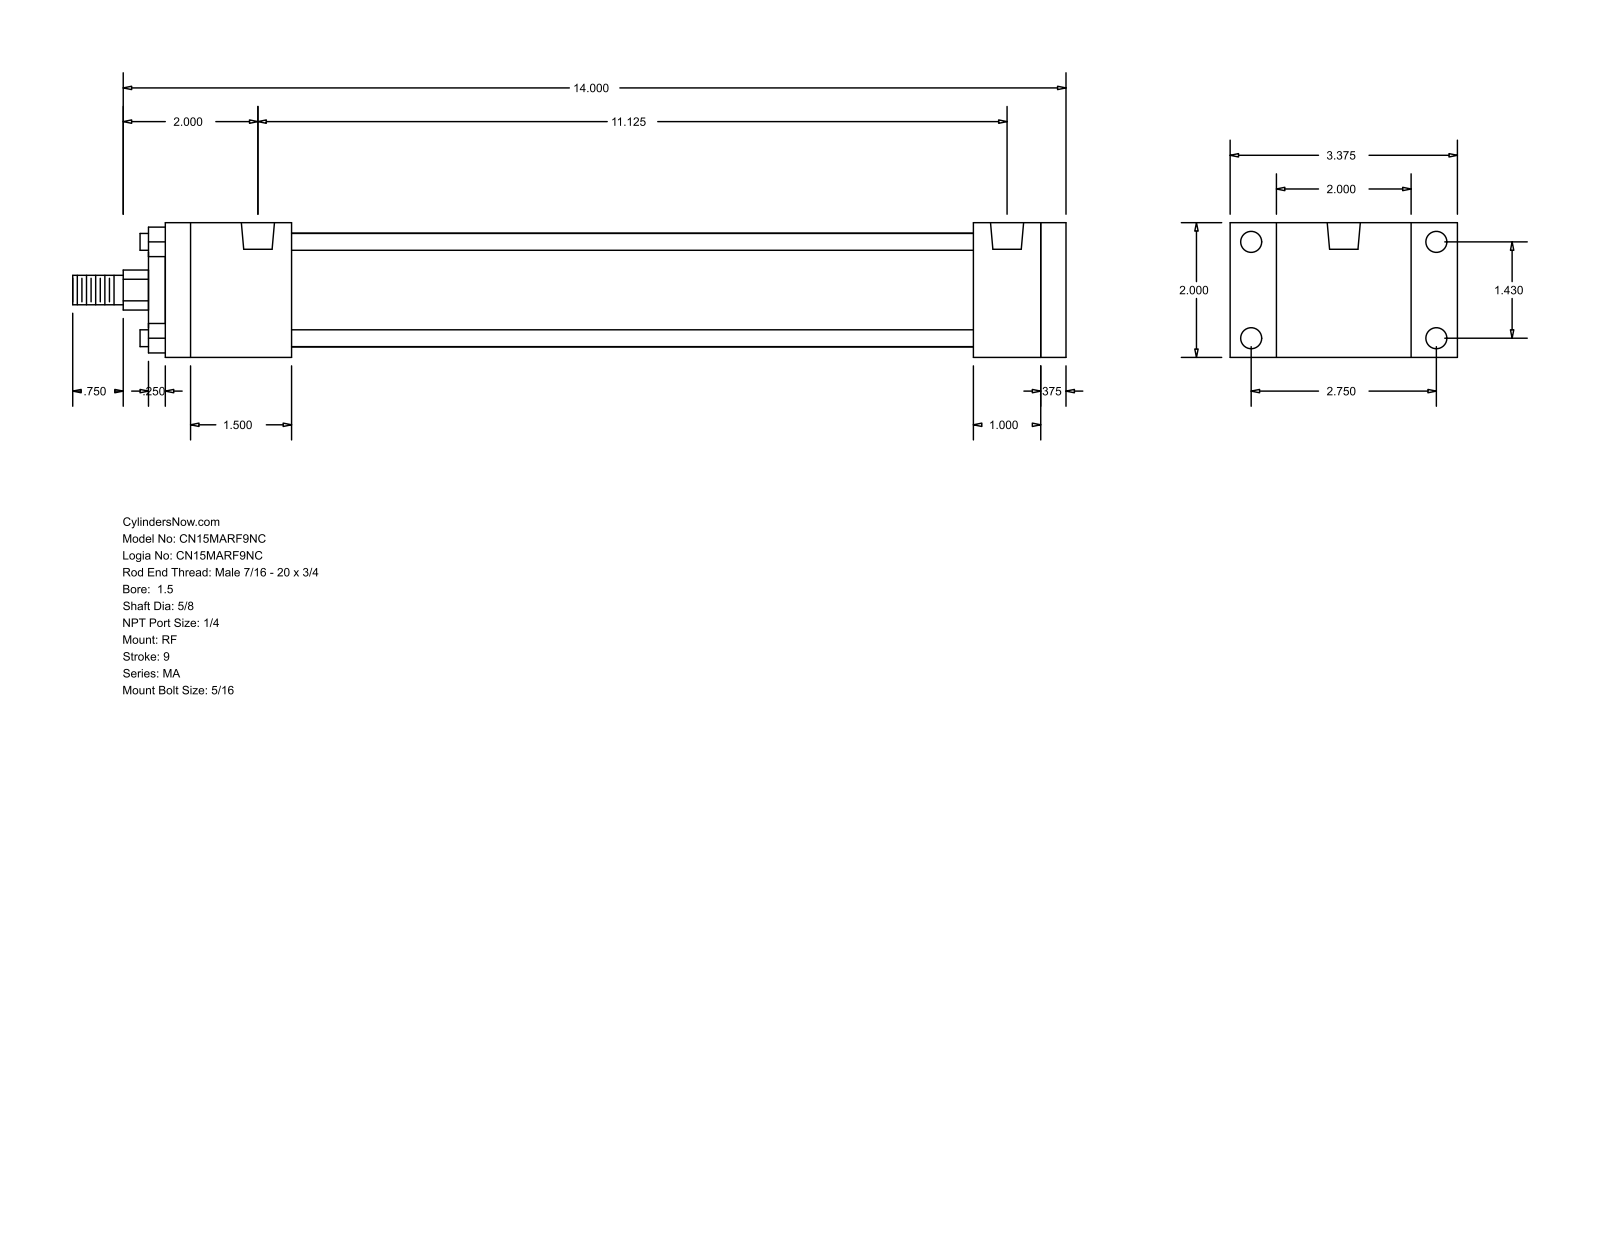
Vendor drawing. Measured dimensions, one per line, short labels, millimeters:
name: MA_RF__0150_0.625
written by: GSSL Pune (CONFIG_CONTROL_DESIGN)
unit: mm
bodies: 0 solids, 92 faces (64 planar, 28 cylindrical, 0 other)
size: 374.65 × 85.72 × 50.8
holes: 8× ⌀7.94, 2× ⌀12.49
bosses: 4× ⌀6.35, 1× ⌀42.93, 1× ⌀28.57, 1× ⌀15.88, 1× ⌀11.11
rounds: 1× R7.54
face distances: 50.8, 9.53, 339.72, 330.19, 304.8, 25.39, 34.92, 47.62, 257.18, 282.57
hole spacings: 36.32, 69.84, 78.72, 282.58
